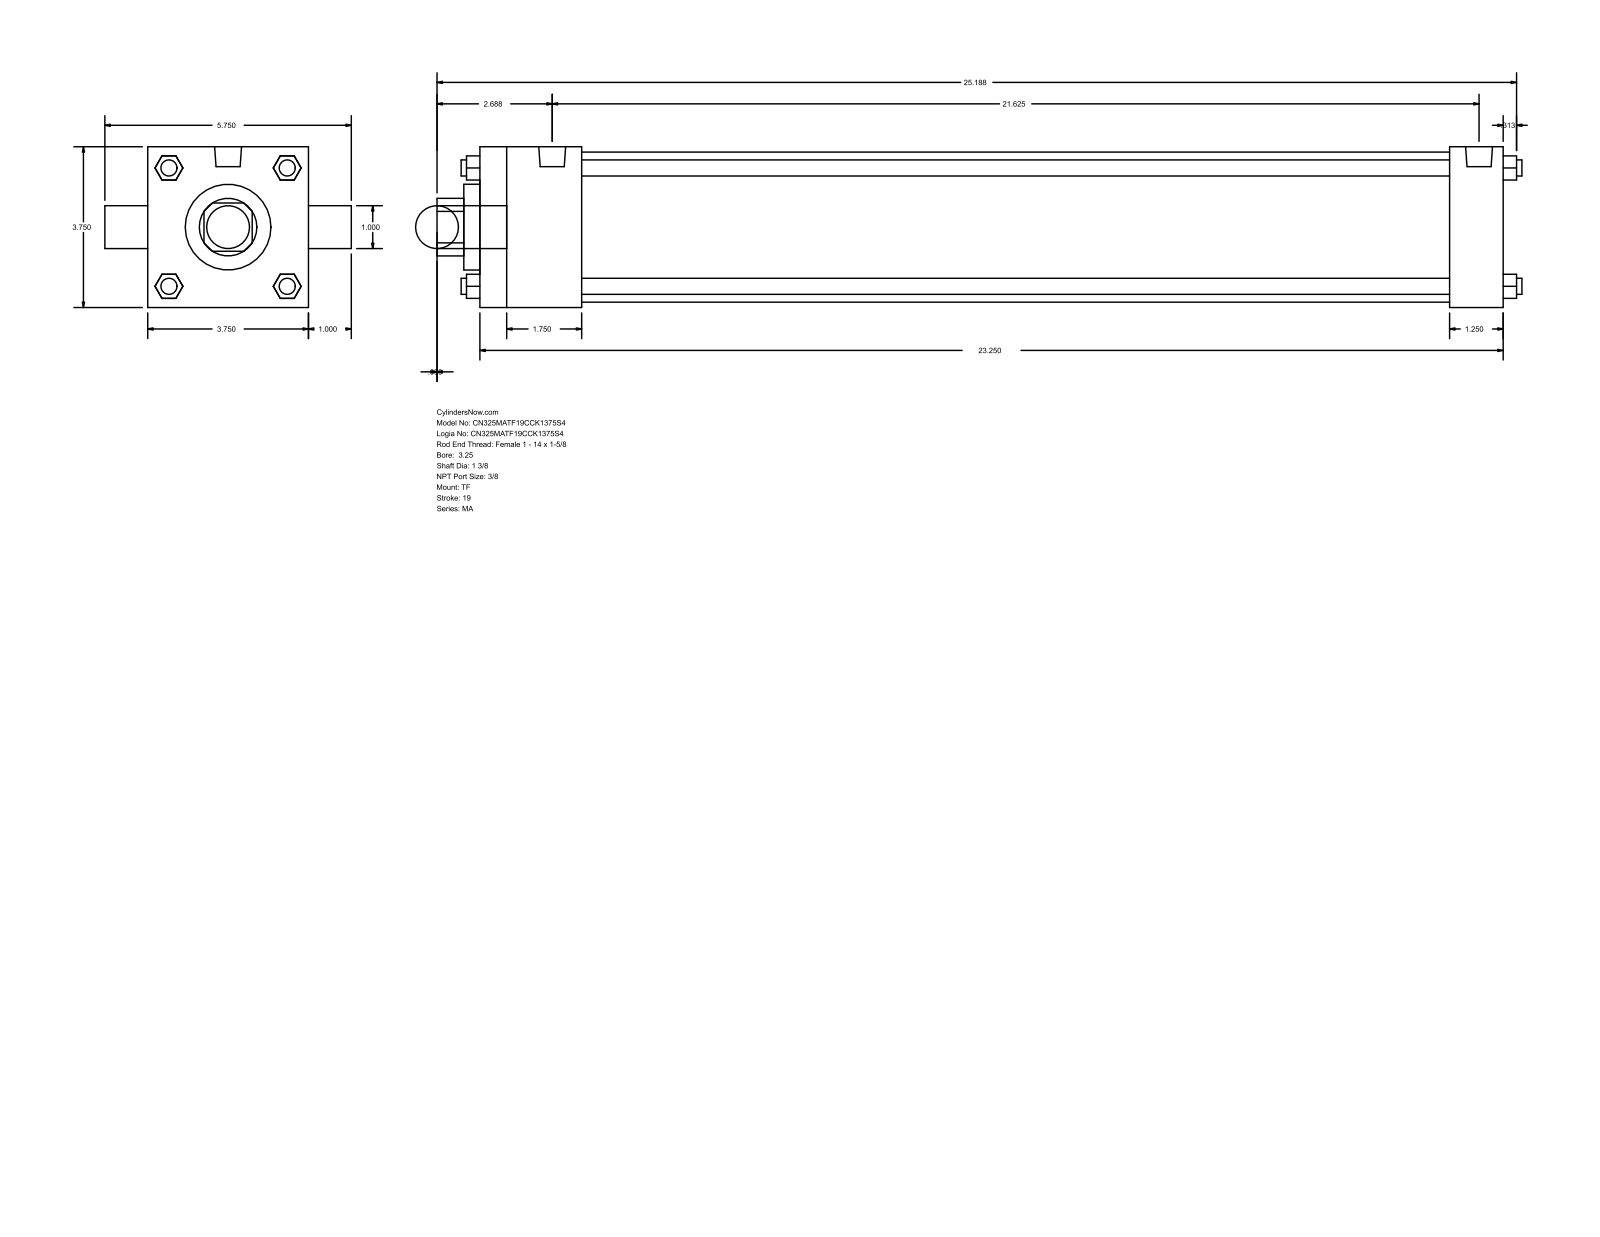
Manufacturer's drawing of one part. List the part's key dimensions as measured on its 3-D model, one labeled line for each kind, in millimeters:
Part name (STEP PRODUCT): MA_TF__0325_1.375
STEP written by: GSSL Pune (CONFIG_CONTROL_DESIGN)
Units: millimetres
Bodies: 0 solids, 120 faces (92 planar, 28 cylindrical, 0 other)
Overall size (bounding box): 642.94 × 146.05 × 95.25
Round holes (diameter × count): ⌀25.4 ×1, ⌀34.92 ×1, ⌀50.8 ×1, ⌀88.9 ×1
Round bosses / shafts (diameter × count): ⌀9.53 ×4, ⌀11.11 ×3, ⌀15.93 ×2, ⌀25.4 ×1
Partial cylindrical surfaces — rounded edges, fillets, slot ends (radius × count): R17.06 ×1
Main face-to-face distances: 95.24, 606.43, 60.32, 574.68, 514.36, 546.11, 31.75, 9.52, 69.84, 584.2
